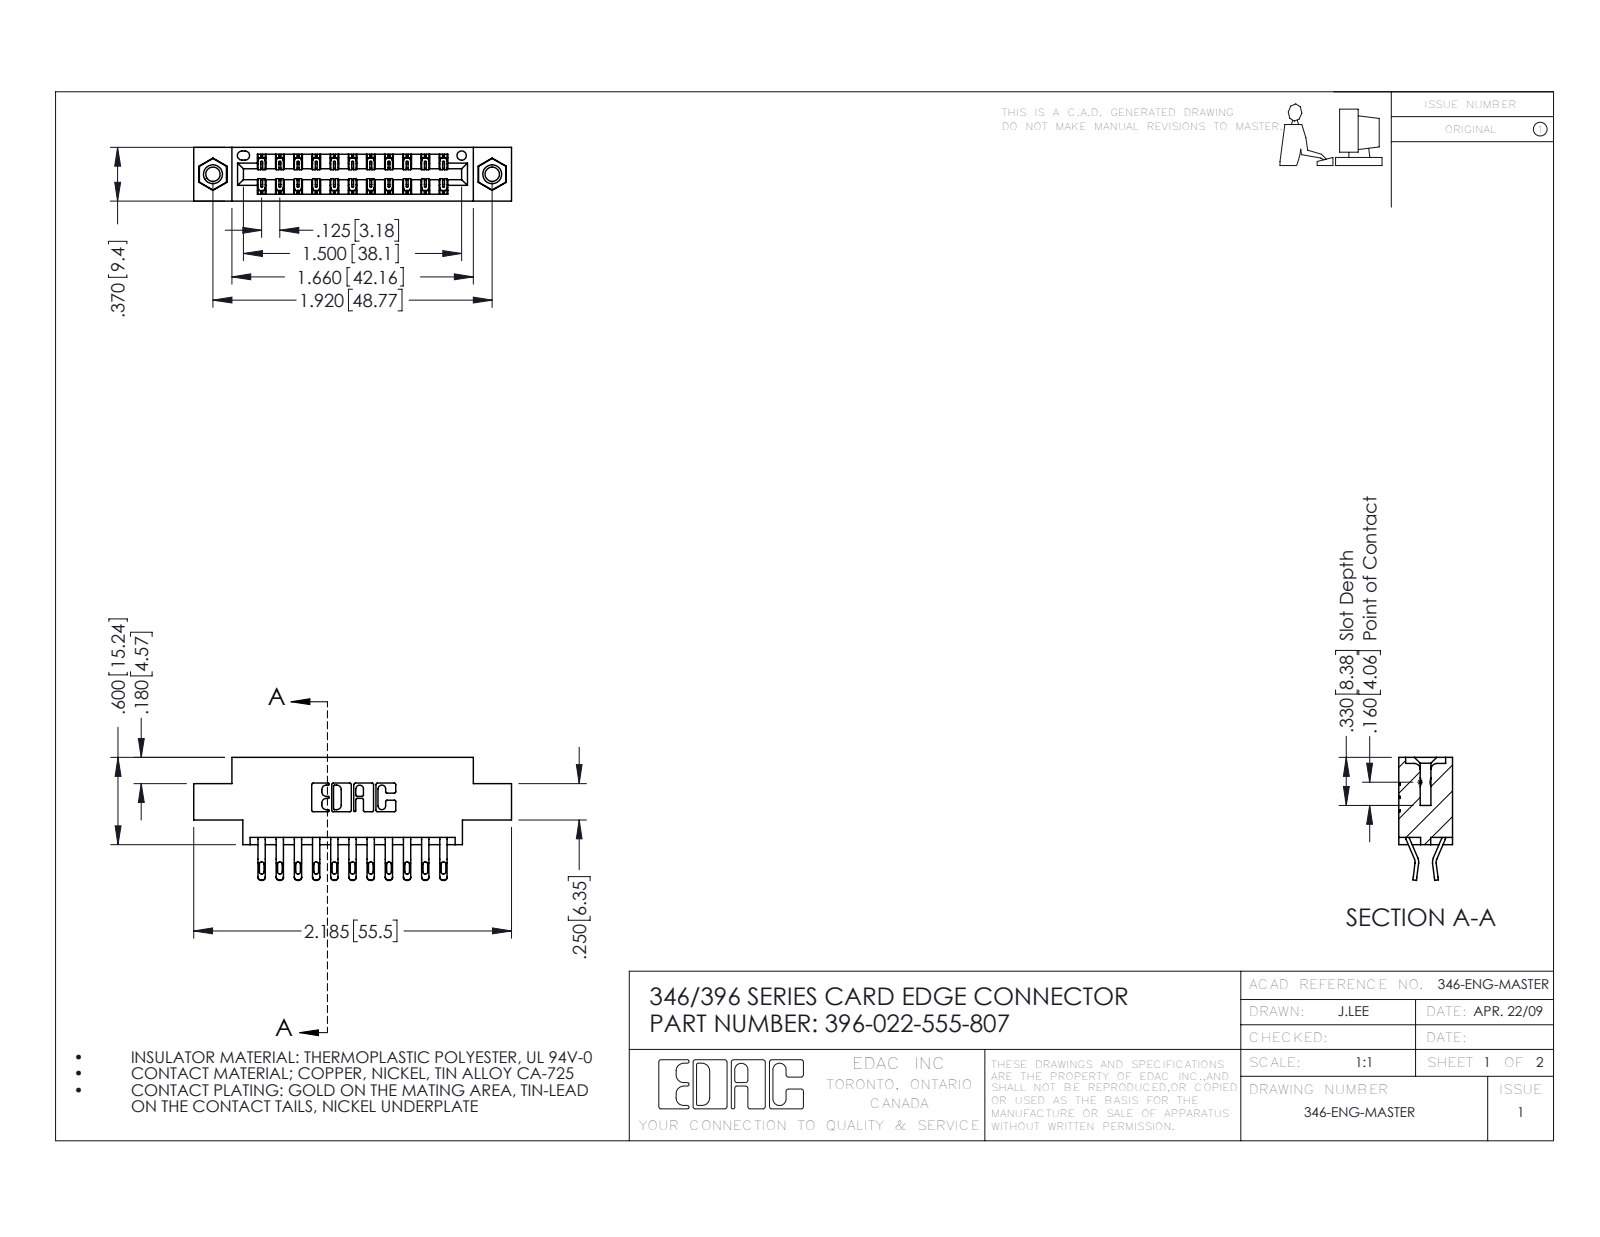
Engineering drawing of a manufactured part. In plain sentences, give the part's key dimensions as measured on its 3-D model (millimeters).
The part is named "346 Part_0.170 Offset - 0.156 Dia-TI; 345-292-001_555 Tail; 345-250-001_345-250-005-103; 396-022-555-807". Its 3-D file was written by "SolidWorks 2016 (CONFIG_CONTROL_DESIGN)". It is 25 solids with 1462 faces: 838 planar, 608 cylindrical and 16 other. Overall it measures 55.5 by 21.5 by 9.4 millimeters. Its volume is 5 060 cubic millimeters and its surface area 6 916 square millimeters. Round holes: 2 of diameter 2.5, 2 of diameter 3.2, 2 of diameter 4, 1 of diameter 1.6. Round bosses or shafts: 2 of diameter 3.9. Partial cylindrical surfaces (rounded edges, fillets, slot ends): 44 of radius 0.4, 44 of radius 0.5, 33 of radius 0.2, 22 of radius 0.3, 6 of radius 0.2, 6 of radius 0.8, 3 of radius 0.7, 2 of radius 0.3. The main face-to-face distances are 6.4, 9.4, 1.2, 8.2, 0.6, 5.6, 3.8, 1.8, 7.6, 7. The hole center spacings are 6.2, 43.6, 48.8.
